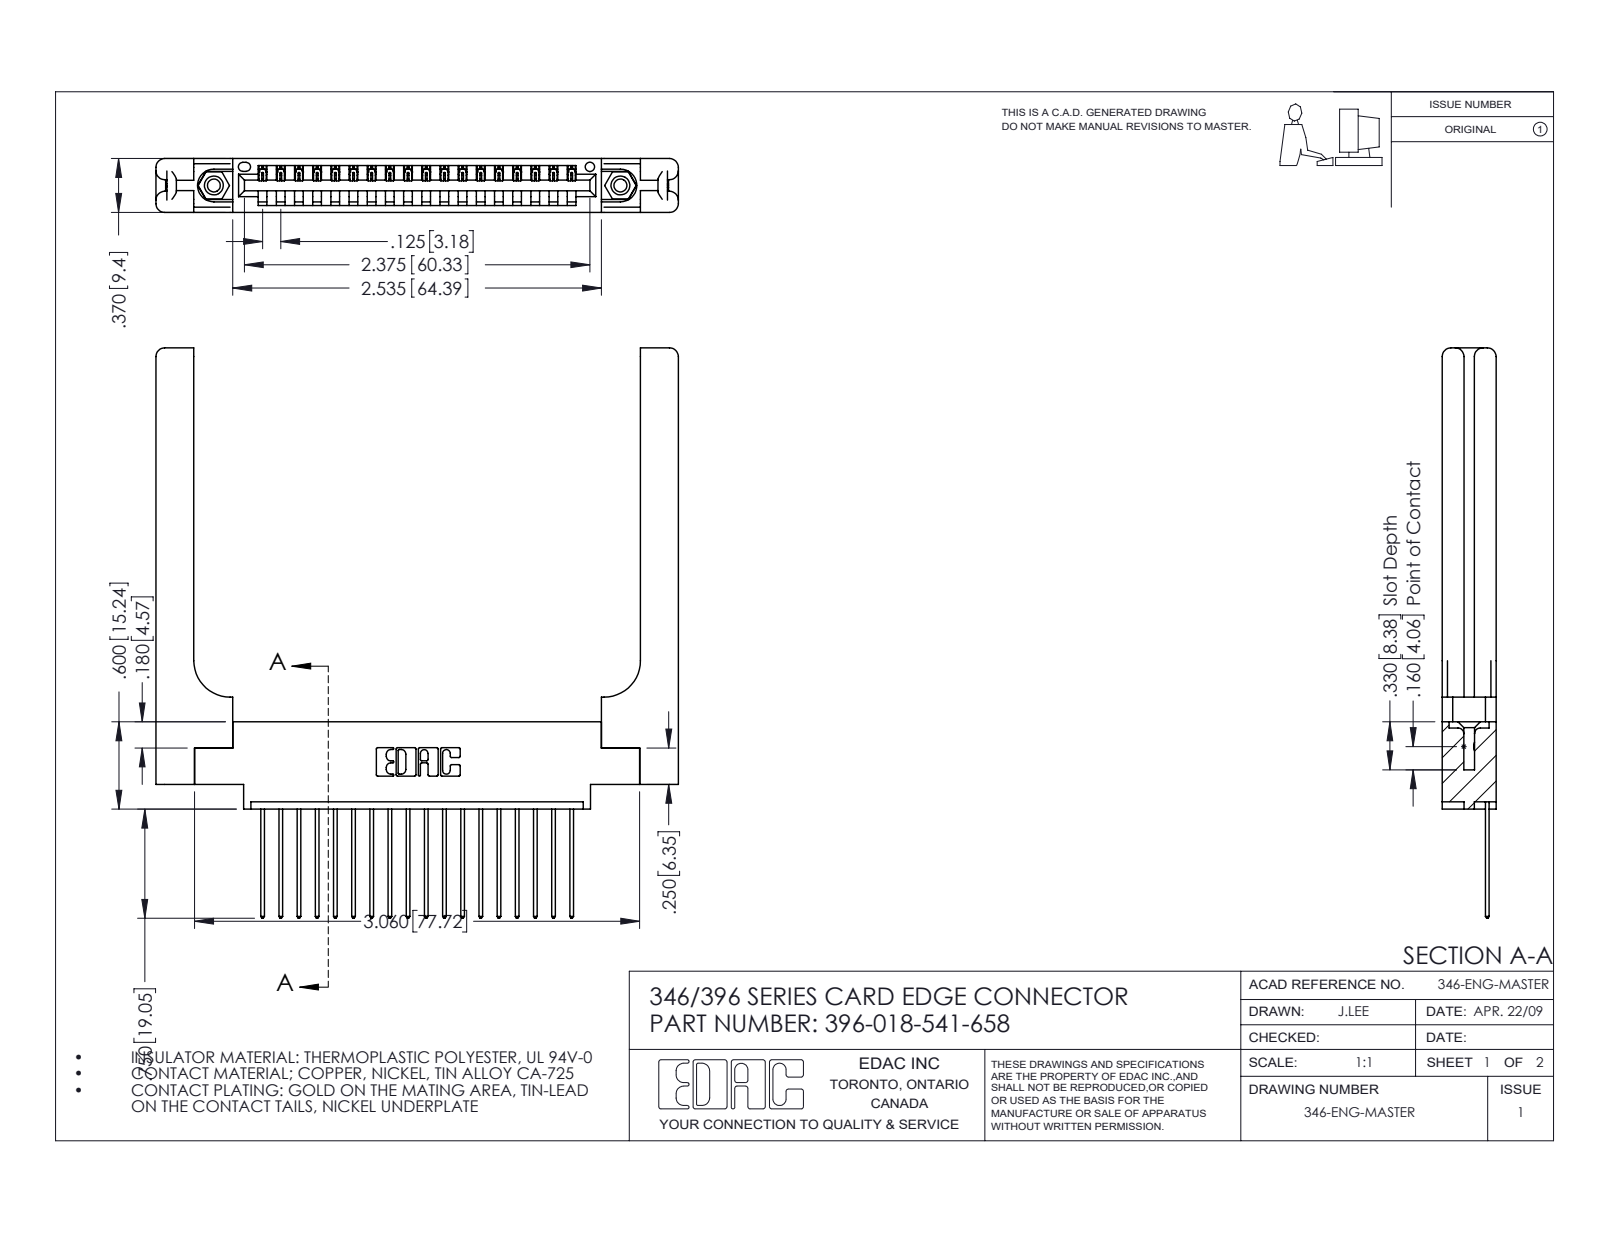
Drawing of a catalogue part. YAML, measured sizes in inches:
part_name: "396-018-541-658; 346-220-058_345-220-058; 345-250-001_345-250-001-102; 345-292-001_345-293-141 (+1 more)"
step_written_by: "SolidWorks 2016 (CONFIG_CONTROL_DESIGN)"
units: inches
bodies: {solids: 23, faces: 1426, planar: 948, cylindrical: 418, other: 60}
overall_size: [3.92, 3.591, 0.37]
volume: 0.976
surface_area: 24.82
round_holes:
  - {diameter: 0.089, count: 2}
  - {diameter: 0.125, count: 2}
  - {diameter: 0.156, count: 2}
  - {diameter: 0.064, count: 1}
round_bosses_or_shafts:
  - {diameter: 0.155, count: 2}
partial_cylinders:
  - {radius: 0.006, count: 36}
  - {radius: 0.01, count: 36}
  - {radius: 0.01, count: 22}
  - {radius: 0.06, count: 16}
  - {radius: 0.007, count: 6}
  - {radius: 0.031, count: 6}
  - {radius: 0.026, count: 3}
  - {radius: 0.03, count: 2}
face_to_face_distances: [0.37, 0.072, 0.15, 0.048, 0.322, 0.148, 0.25, 0.298, 0.025, 0.102]
hole_center_spacings: [0.246, 2.588, 2.795]
